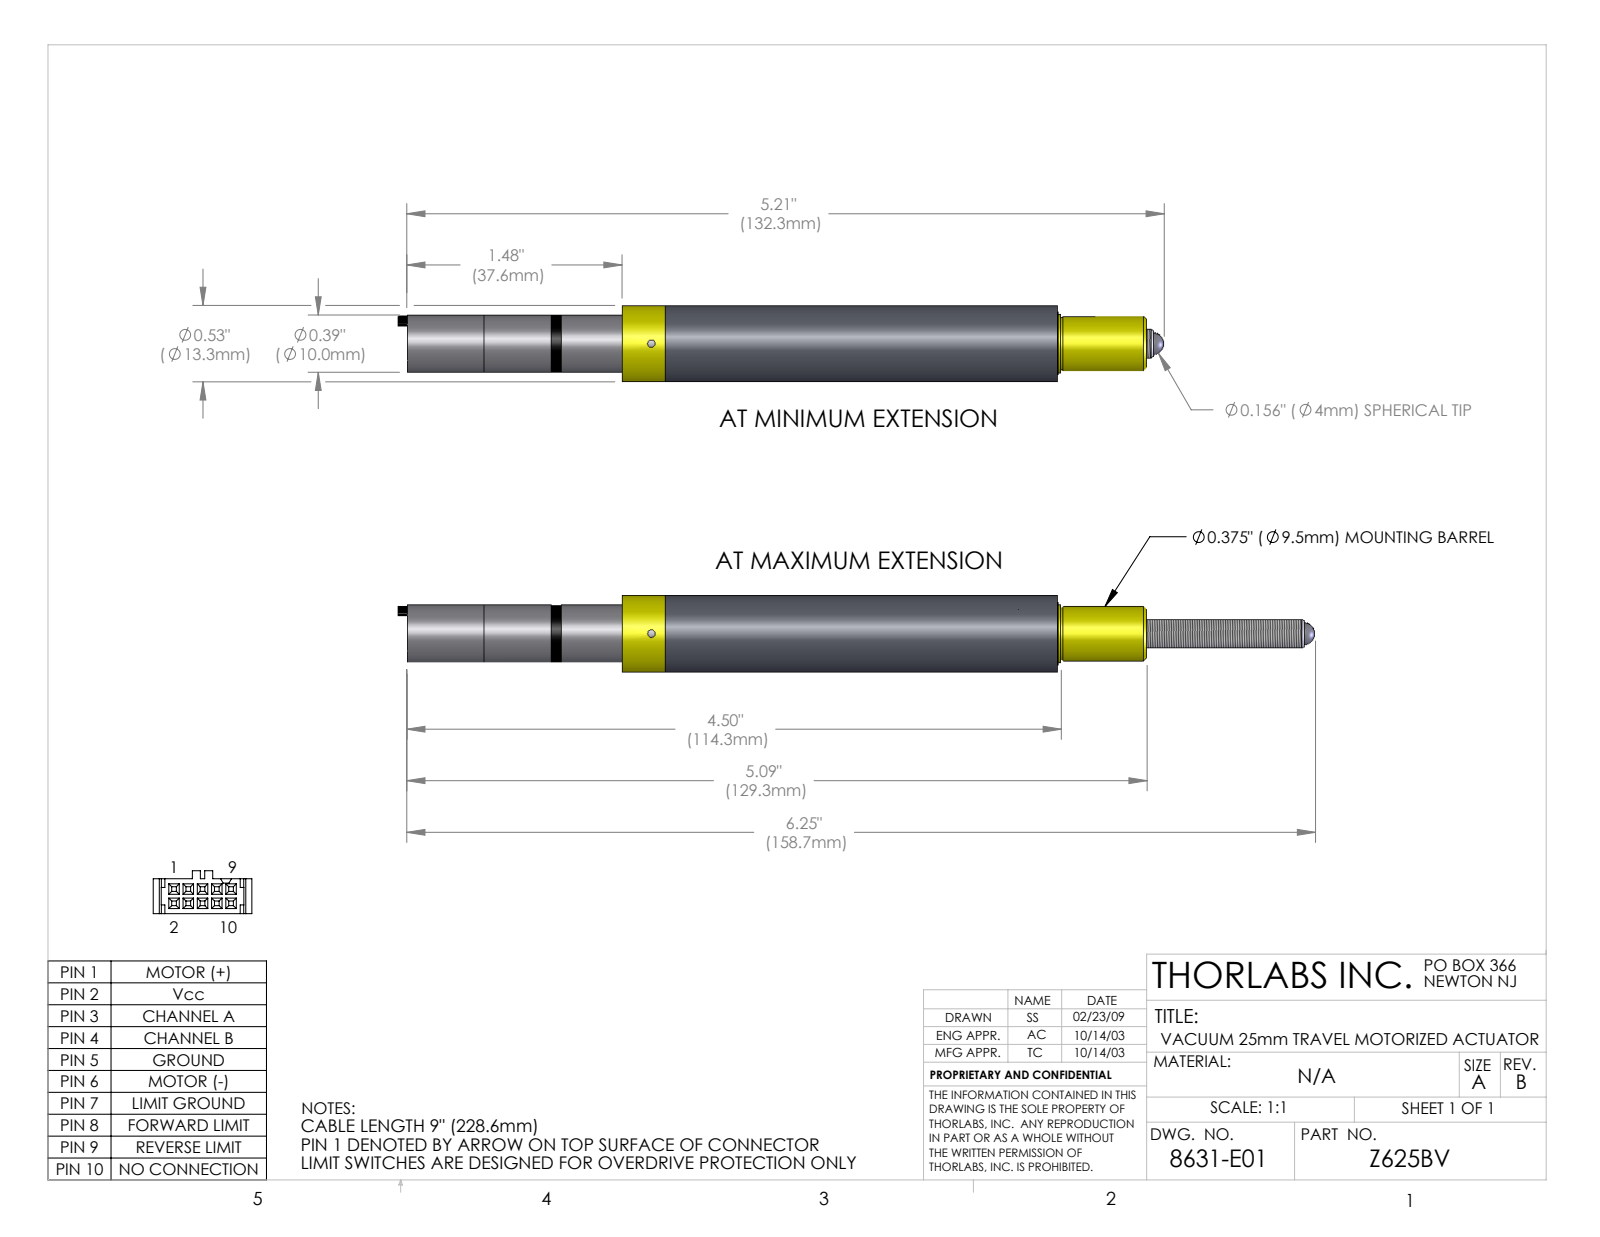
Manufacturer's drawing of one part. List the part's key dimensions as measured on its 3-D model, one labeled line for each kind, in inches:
Part name (STEP PRODUCT): 8631-E0W
STEP written by: SolidWorks 2007 (AUTOMOTIVE_DESIGN)
Units: inches
Bodies: 6 solids, 203 faces (90 planar, 95 cylindrical, 18 other)
Overall size (bounding box): 5.27 × 0.525 × 0.525
Volume: 0.596 in³ · Surface area: 24.83 in²
Round holes (diameter × count): ⌀0.052 ×1, ⌀0.156 ×1, ⌀0.18 ×1, ⌀0.197 ×1, ⌀0.2 ×1, ⌀0.375 ×1, ⌀0.433 ×1, ⌀0.48 ×1, ⌀0.495 ×1, ⌀0.505 ×1
Round bosses / shafts (diameter × count): ⌀0.525 ×1, ⌀0.504 ×1, ⌀0.44 ×1, ⌀0.433 ×1, ⌀0.403 ×1, ⌀0.393 ×1, ⌀0.393 ×1, ⌀0.393 ×1
Partial cylindrical surfaces — rounded edges, fillets, slot ends (radius × count): R0.062 ×6, R0.063 ×4, R0.008 ×3, R0.031 ×2, R0.047 ×2, R0.172 ×1, R0.189 ×1, R0.198 ×1
Main face-to-face distances: 0.018, 0.094, 0.054, 0.036, 0.036, 0.072, 0.018, 0.09, 1.06, 0.75
